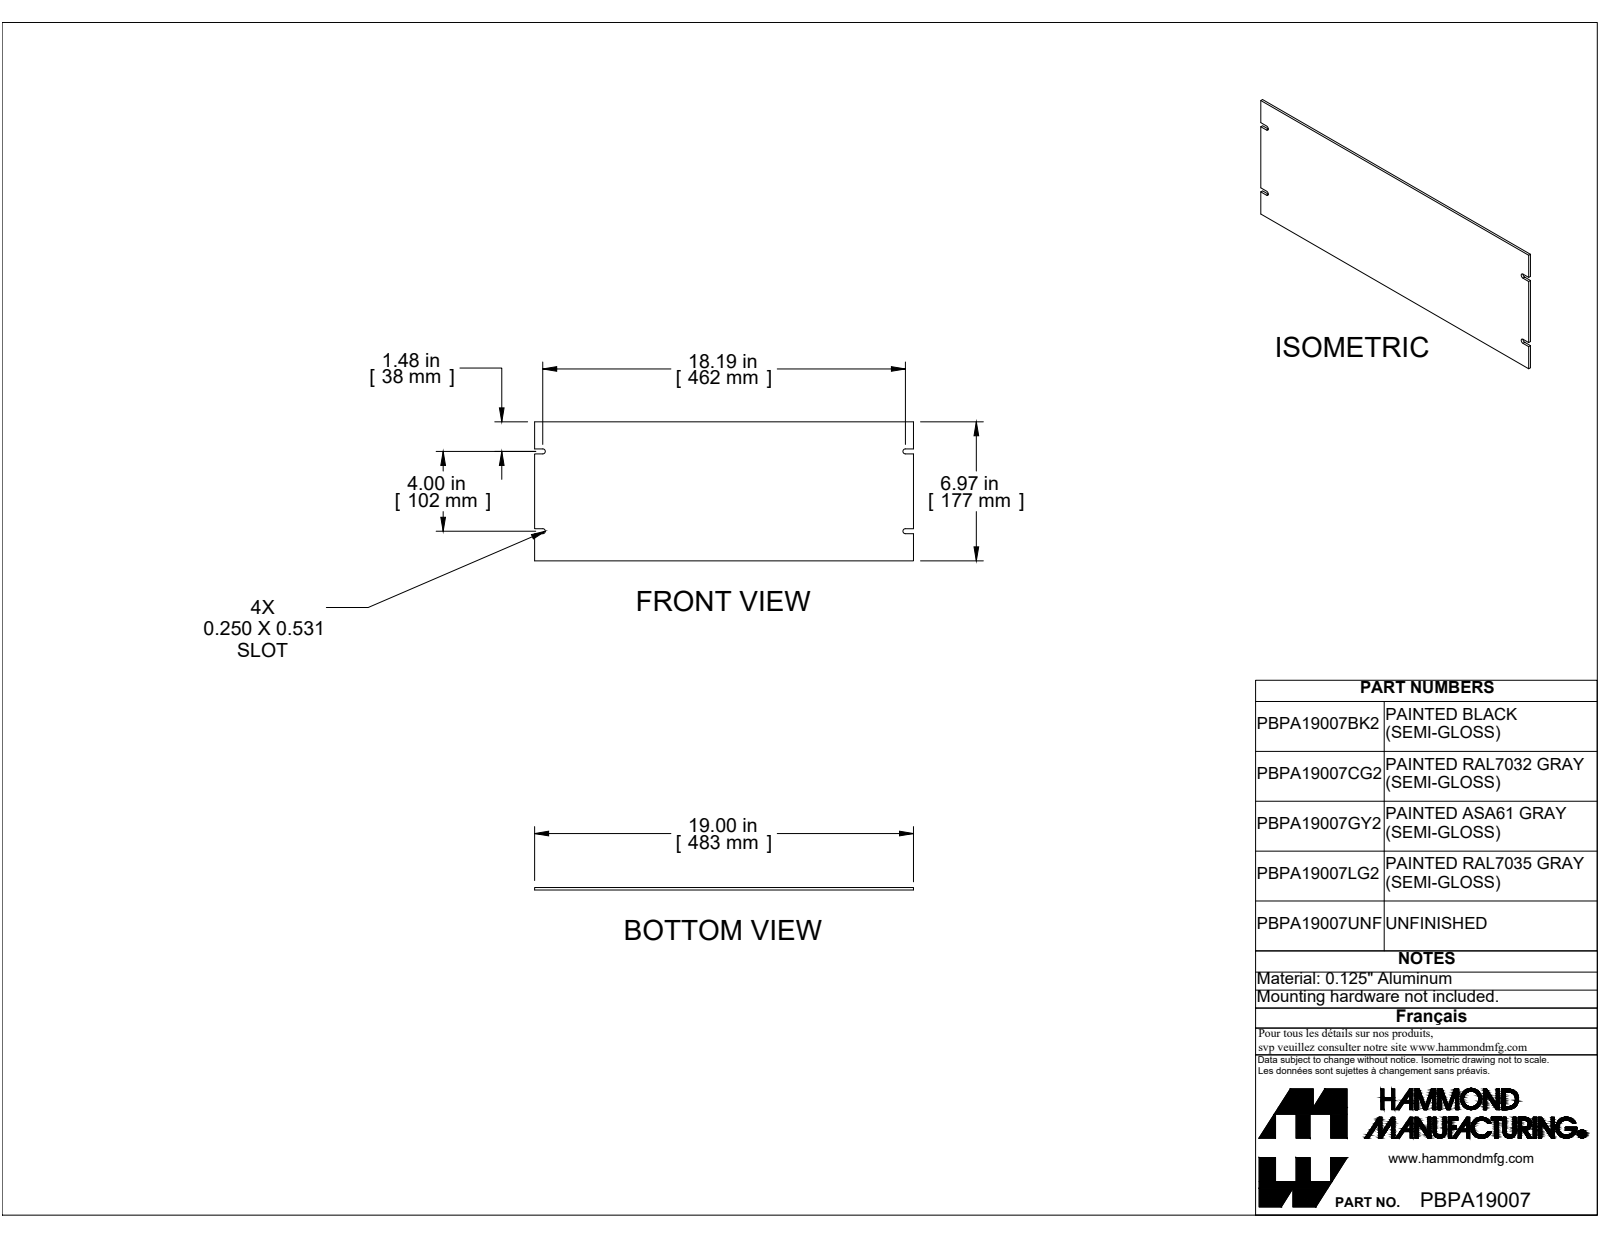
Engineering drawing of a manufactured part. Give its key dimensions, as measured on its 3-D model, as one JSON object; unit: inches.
{"part_name": "PBPA19007BK2", "step_written_by": "SolidWorks 2019 (CONFIG_CONTROL_DESIGN)", "units": "inches", "bodies": {"solids": 1, "faces": 22, "planar": 18, "cylindrical": 4, "other": 0}, "overall_size": [19, 6.968, 0.125], "volume_in3": 16.49, "surface_area_in2": 270.7, "partial_cylinders_radius": [[0.125, 4]], "face_to_face_distances": [0.125, 6.968, 19, 1.609, 5.359, 1.359, 5.609, 4, 0.25, 3.75]}
